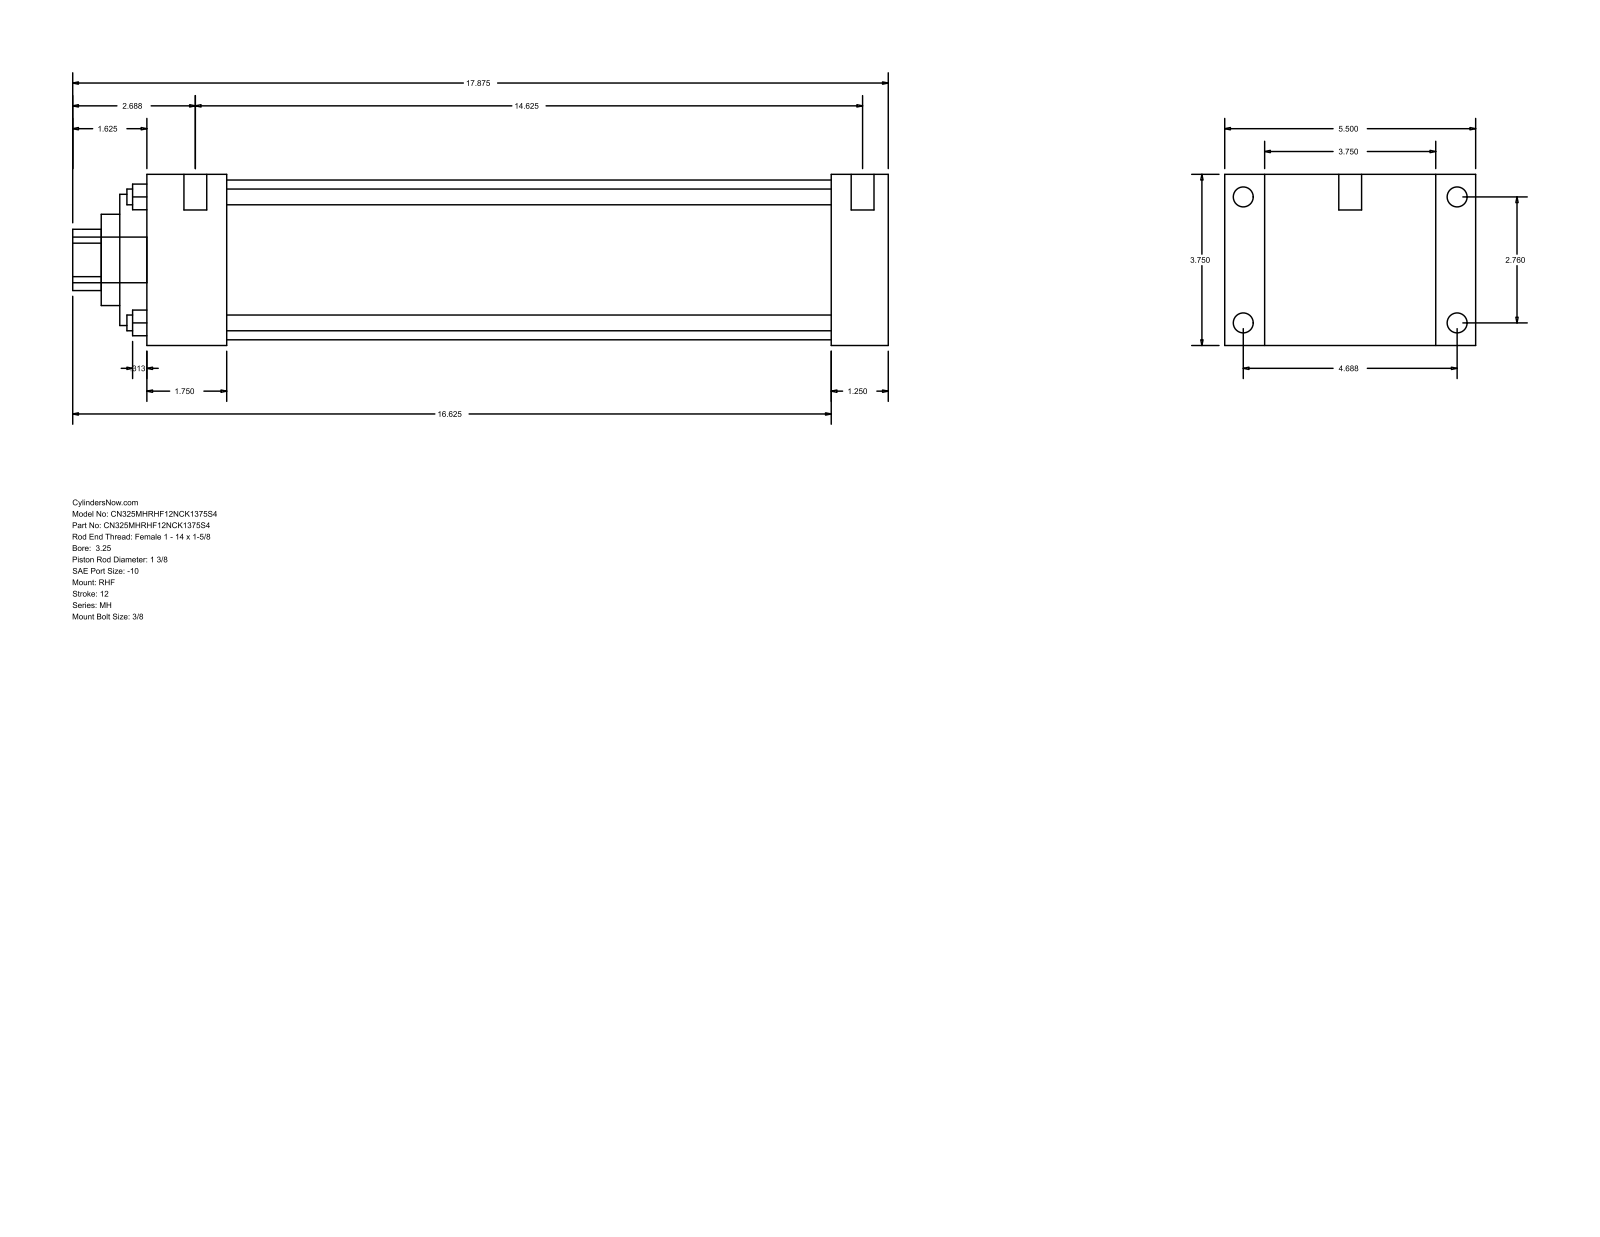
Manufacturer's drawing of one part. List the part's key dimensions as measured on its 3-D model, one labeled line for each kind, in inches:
Part name (STEP PRODUCT): MH_RHF__0325_1.375
STEP written by: GSSL Pune (CONFIG_CONTROL_DESIGN)
Units: inches
Bodies: 0 solids, 90 faces (61 planar, 29 cylindrical, 0 other)
Overall size (bounding box): 17.875 × 5.5 × 3.75
Round holes (diameter × count): ⌀0.345 ×4, ⌀1.375 ×1, ⌀2 ×1, ⌀2.875 ×1, ⌀3.5 ×1
Round bosses / shafts (diameter × count): ⌀0.438 ×4, ⌀0.219 ×4, ⌀0.5 ×2, ⌀1 ×1
Partial cylindrical surfaces — rounded edges, fillets, slot ends (radius × count): R0.672 ×1
Main face-to-face distances: 3.75, 1.25, 0.875, 4.625, 15, 16.25, 5.5, 1.75, 13.25, 14.5
Hole centre spacings: 1.952, 2.76, 3.903
